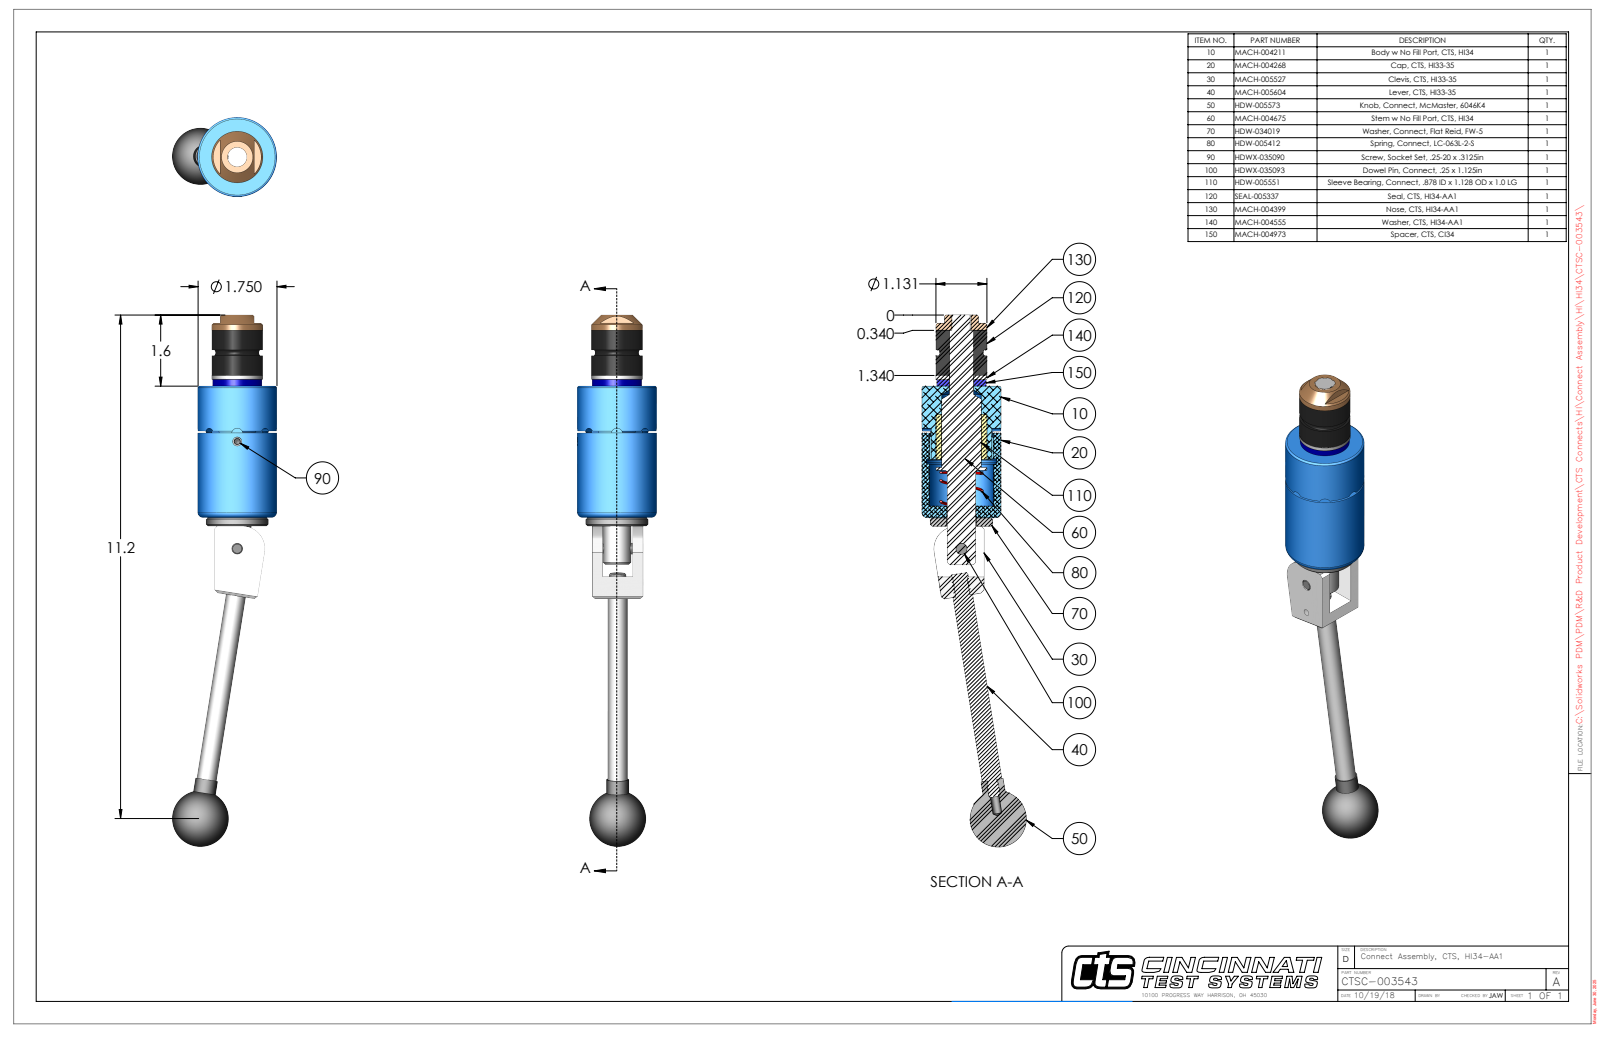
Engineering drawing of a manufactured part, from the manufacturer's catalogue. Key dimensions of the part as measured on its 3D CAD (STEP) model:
Part name (STEP PRODUCT): CTSC-003543
STEP written by: SolidWorks 2023 (AUTOMOTIVE_DESIGN)
Units: inches
Bodies: 10 solids, 254 faces (93 planar, 102 cylindrical, 59 other)
Overall size (bounding box): 11.792 × 2.312 × 1.75
Volume: 11.65 in³ · Surface area: 69.47 in²
Round holes (diameter × count): ⌀0.201 ×2, ⌀0.15 ×1, ⌀0.249 ×1, ⌀0.251 ×1, ⌀0.313 ×1, ⌀0.422 ×1, ⌀0.53 ×1, ⌀0.541 ×1, ⌀0.547 ×1, ⌀0.635 ×1, ⌀0.656 ×1, ⌀1.419 ×1
Round bosses / shafts (diameter × count): ⌀0.5 ×2, ⌀0.44 ×2, ⌀0.25 ×2, ⌀1.75 ×1, ⌀1.38 ×1, ⌀1.131 ×1, ⌀1.09 ×1, ⌀0.625 ×1
Partial cylindrical surfaces — rounded edges, fillets, slot ends (radius × count): R0.125 ×4, R0.029 ×2, R0.5 ×1, R0.695 ×1, R0.829 ×1
Main face-to-face distances: 2.918, 1.237, 1, 4.155, 0.237, 3.155, 1.12, 1.094, 0.094, 0.143
Hole centre spacings: 0.74, 2.376, 3.116
